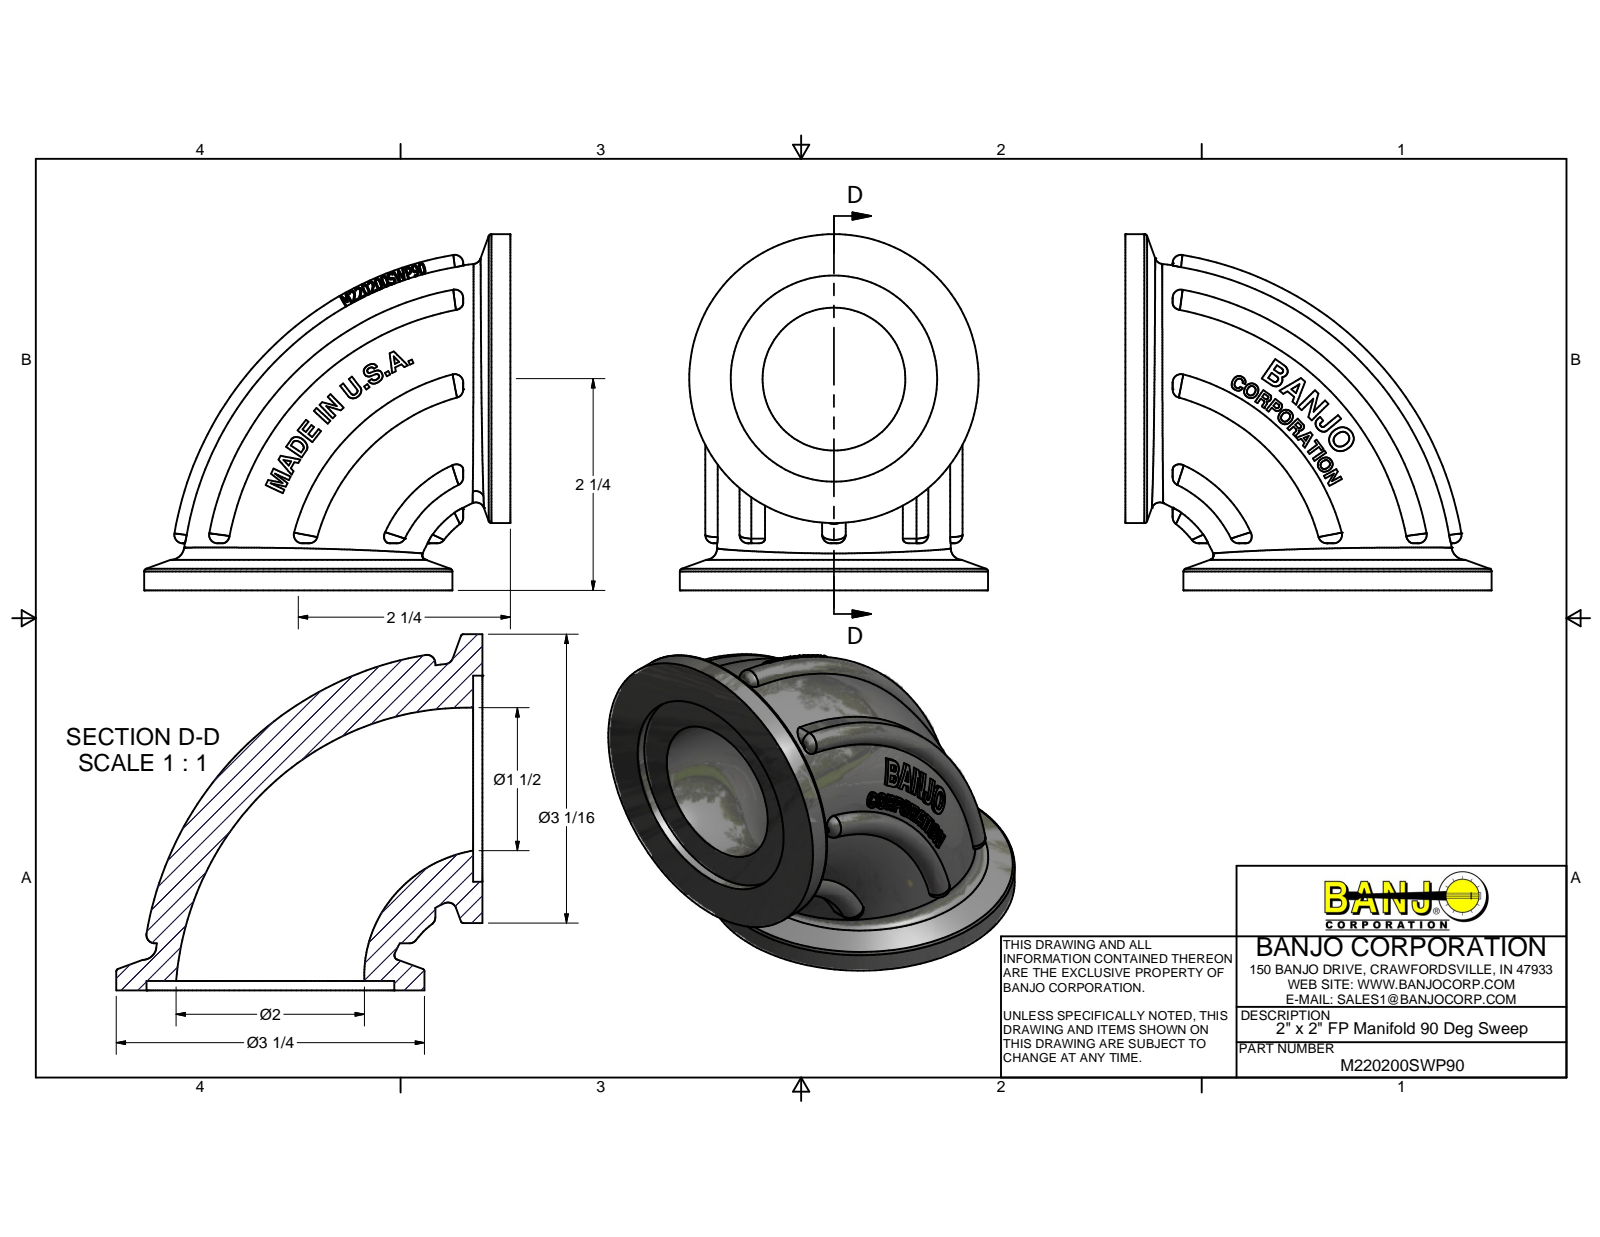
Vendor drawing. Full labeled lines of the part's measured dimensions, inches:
Part name (STEP PRODUCT): M220200SWP90
STEP written by: Autodesk Inventor 2011 (AUTOMOTIVE_DESIGN)
Units: inches
Bodies: 1 solid, 626 faces (270 planar, 16 cylindrical, 340 other)
Overall size (bounding box): 3.885 × 3.785 × 3.27
Volume: 10.29 in³ · Surface area: 67.38 in²
Round holes (diameter × count): ⌀2.19 ×1, ⌀2.63 ×1
Round bosses / shafts (diameter × count): ⌀3.27 ×1, ⌀3.07 ×1
Partial cylindrical surfaces — rounded edges, fillets, slot ends (radius × count): R0.09 ×4, R1.248 ×1, R3.252 ×1
Main face-to-face distances: 0.1, 0.5, 0.4, 0.041, 0.052, 0.041, 0.2, 0.031, 0.035, 0.152
